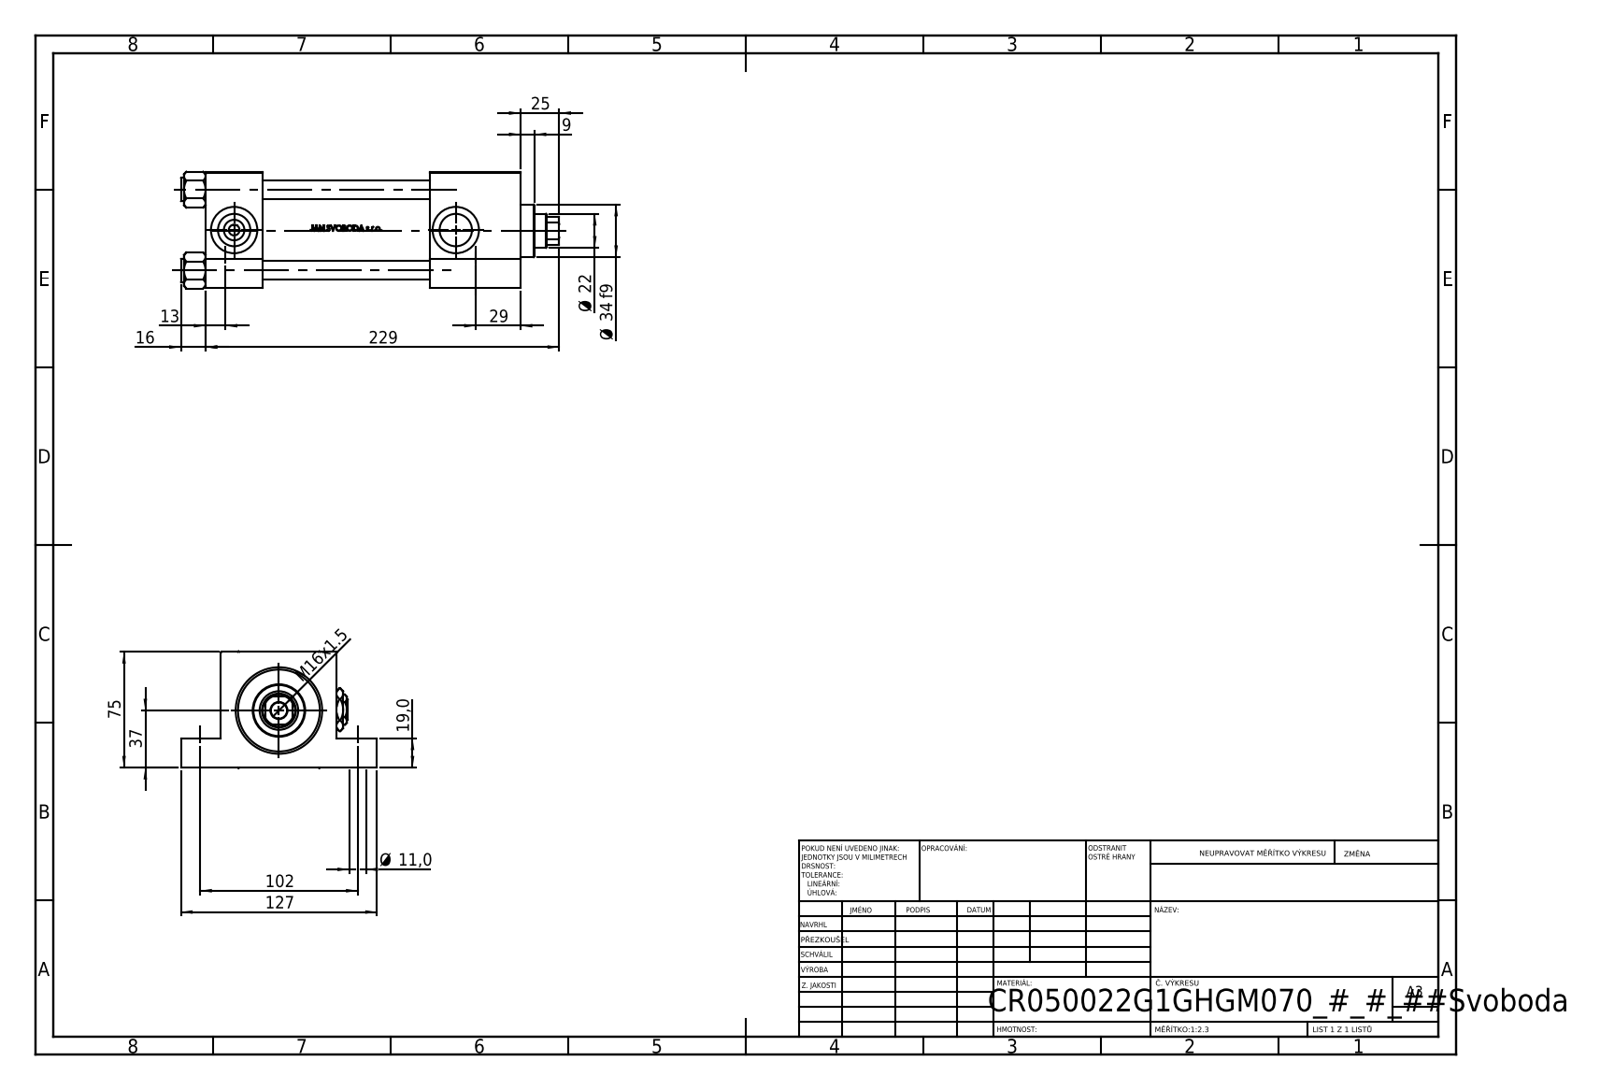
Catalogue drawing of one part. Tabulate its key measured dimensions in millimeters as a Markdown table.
| quantity | value |
| --- | --- |
| part name | V215CR_VCP_G; V215CR_G_TYCINKA; V215_VC_A; Zatka_pro_OIL_PORT (+2 more) |
| STEP written by | SolidWorks 2019 (CONFIG_CONTROL_DESIGN) |
| units | millimeters |
| bodies | 12 solids, 1134 faces (454 planar, 128 cylindrical, 552 other) |
| overall size | 245 × 127 × 75.54 |
| volume | 819 005 mm³ |
| surface area | 188 950 mm² |
| round holes (diameter × count) | 11 × 4, 12 × 4, 7 × 2, 20.96 × 2, 30 × 2, 10.5 × 1, 22 × 1, 25 × 1, 41 × 1, 50 × 1, 53 × 1 |
| round bosses / shafts (diameter × count) | 15 × 4, 56 × 1, 34 × 1 |
| partial cylindrical surfaces (radius × count) | 10.5 × 1 |
| main face-to-face distances | 75, 37, 204, 167, 19, 56, 108, 145, 59, 26 |
| hole center spacings | 52.3, 36.63, 37.34, 73.96, 102, 162, 191.44, 143.5 |
